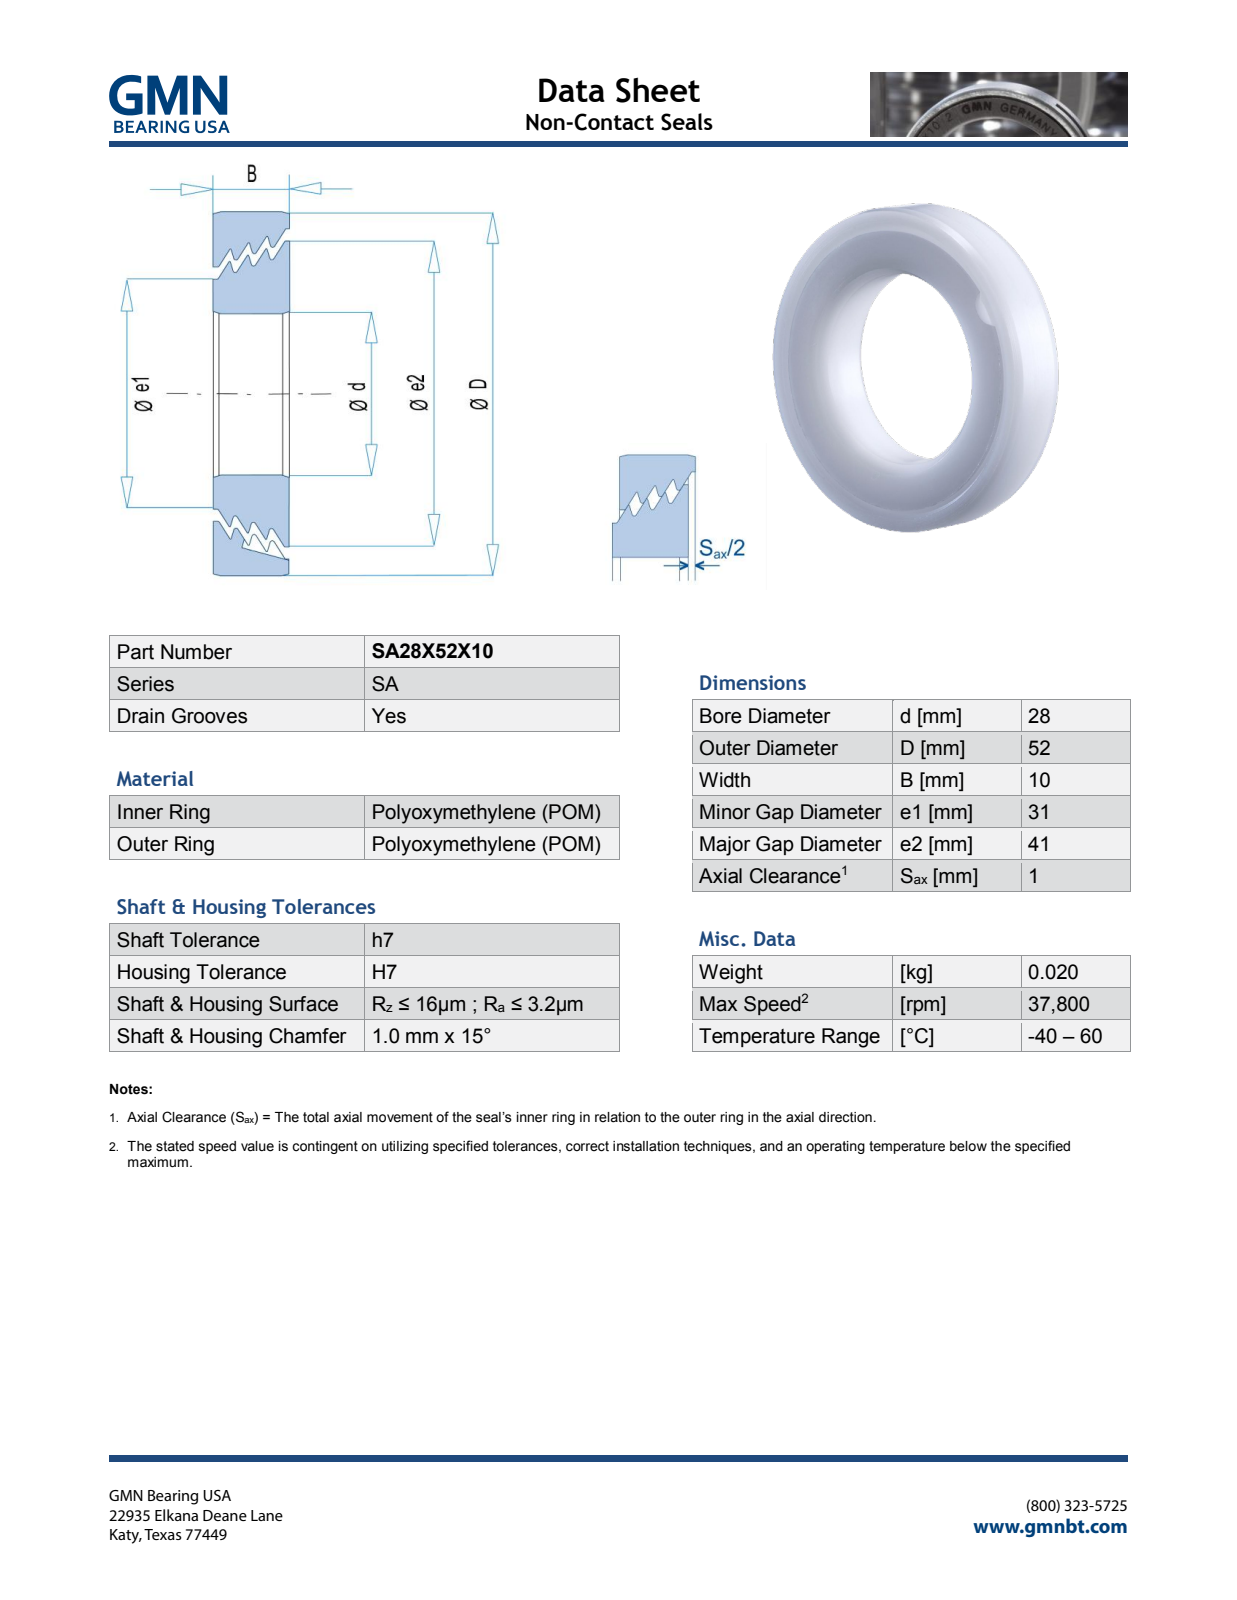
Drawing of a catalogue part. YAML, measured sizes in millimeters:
part_name: "SA28X52X10_PRT"
step_written_by: "PRO/ENGINEER BY PARAMETRIC TECHNOLOGY CORPORATION, 2013150 (AUTOMOTIVE_DESIGN)"
units: millimeters
bodies: {solids: 2, faces: 672, planar: 595, cylindrical: 15, other: 62}
overall_size: [52, 52, 10.07]
volume: 14034
surface_area: 9968
round_holes:
  - {diameter: 28, count: 1}
  - {diameter: 32.63, count: 1}
  - {diameter: 42.63, count: 1}
round_bosses_or_shafts:
  - {diameter: 52, count: 1}
  - {diameter: 41, count: 1}
  - {diameter: 31, count: 1}
partial_cylinders:
  - {radius: 6, count: 1}
face_to_face_distances: [10, 10.07, 1.68, 1.47, 1.26, 1.69, 1.2, 0.75, 1.48, 1.41]
